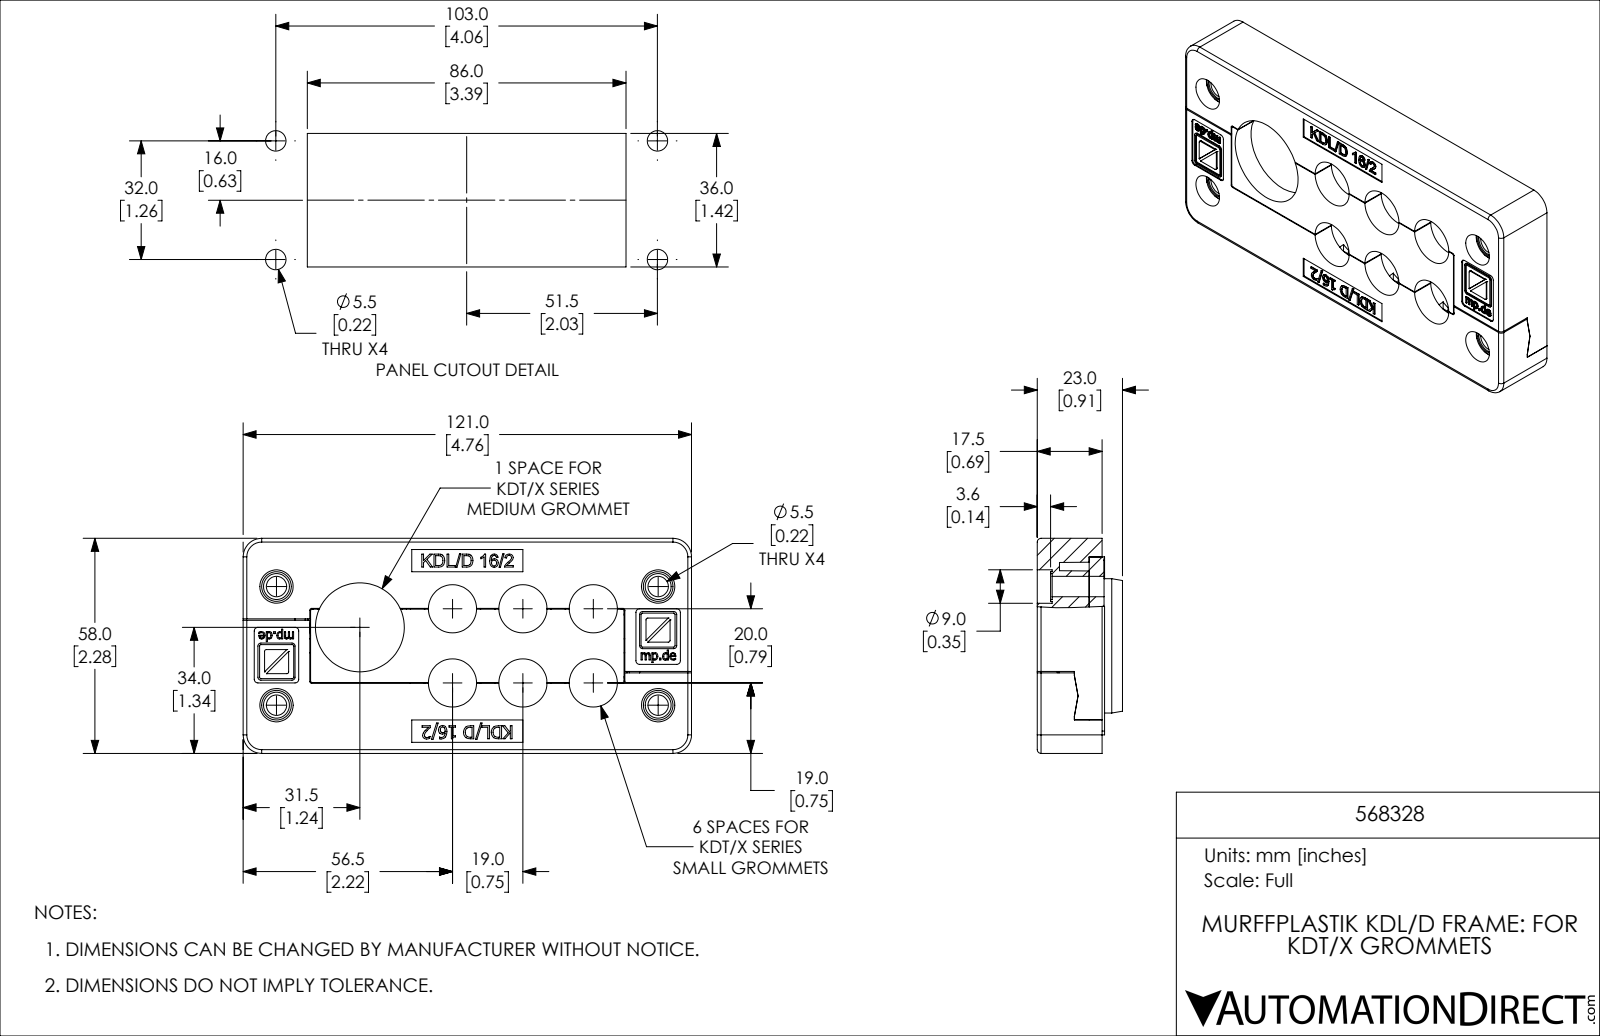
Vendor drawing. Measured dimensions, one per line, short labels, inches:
name: 568328
written by: SolidWorks 2019 (CONFIG_CONTROL_DESIGN)
unit: in
bodies: 4 solids, 1456 faces (818 planar, 258 cylindrical, 380 other)
size: 4.764 × 2.283 × 0.906
volume: 5.642 in³; area: 76.52 in²
holes: 6× ⌀0.197, 6× ⌀0.512, 6× ⌀0.589, 4× ⌀0.217, 4× ⌀0.276, 4× ⌀0.354, 2× ⌀0.236, 1× ⌀0.945, 1× ⌀0.982
bosses: 4× ⌀0.315
rounds: 35× R0.02, 30× R0.039, 12× R0.016, 8× R0.031, 4× R0.004, 4× R0.006, 4× R0.012, 4× R0.197
face distances: 0.157, 0.197, 0.551, 0.138, 0.236, 0.02, 0.709, 0.472, 0.453, 2.283
hole spacings: 0.748, 0.394, 0.443, 0.665, 0.866, 1.086, 0.295, 0.787
